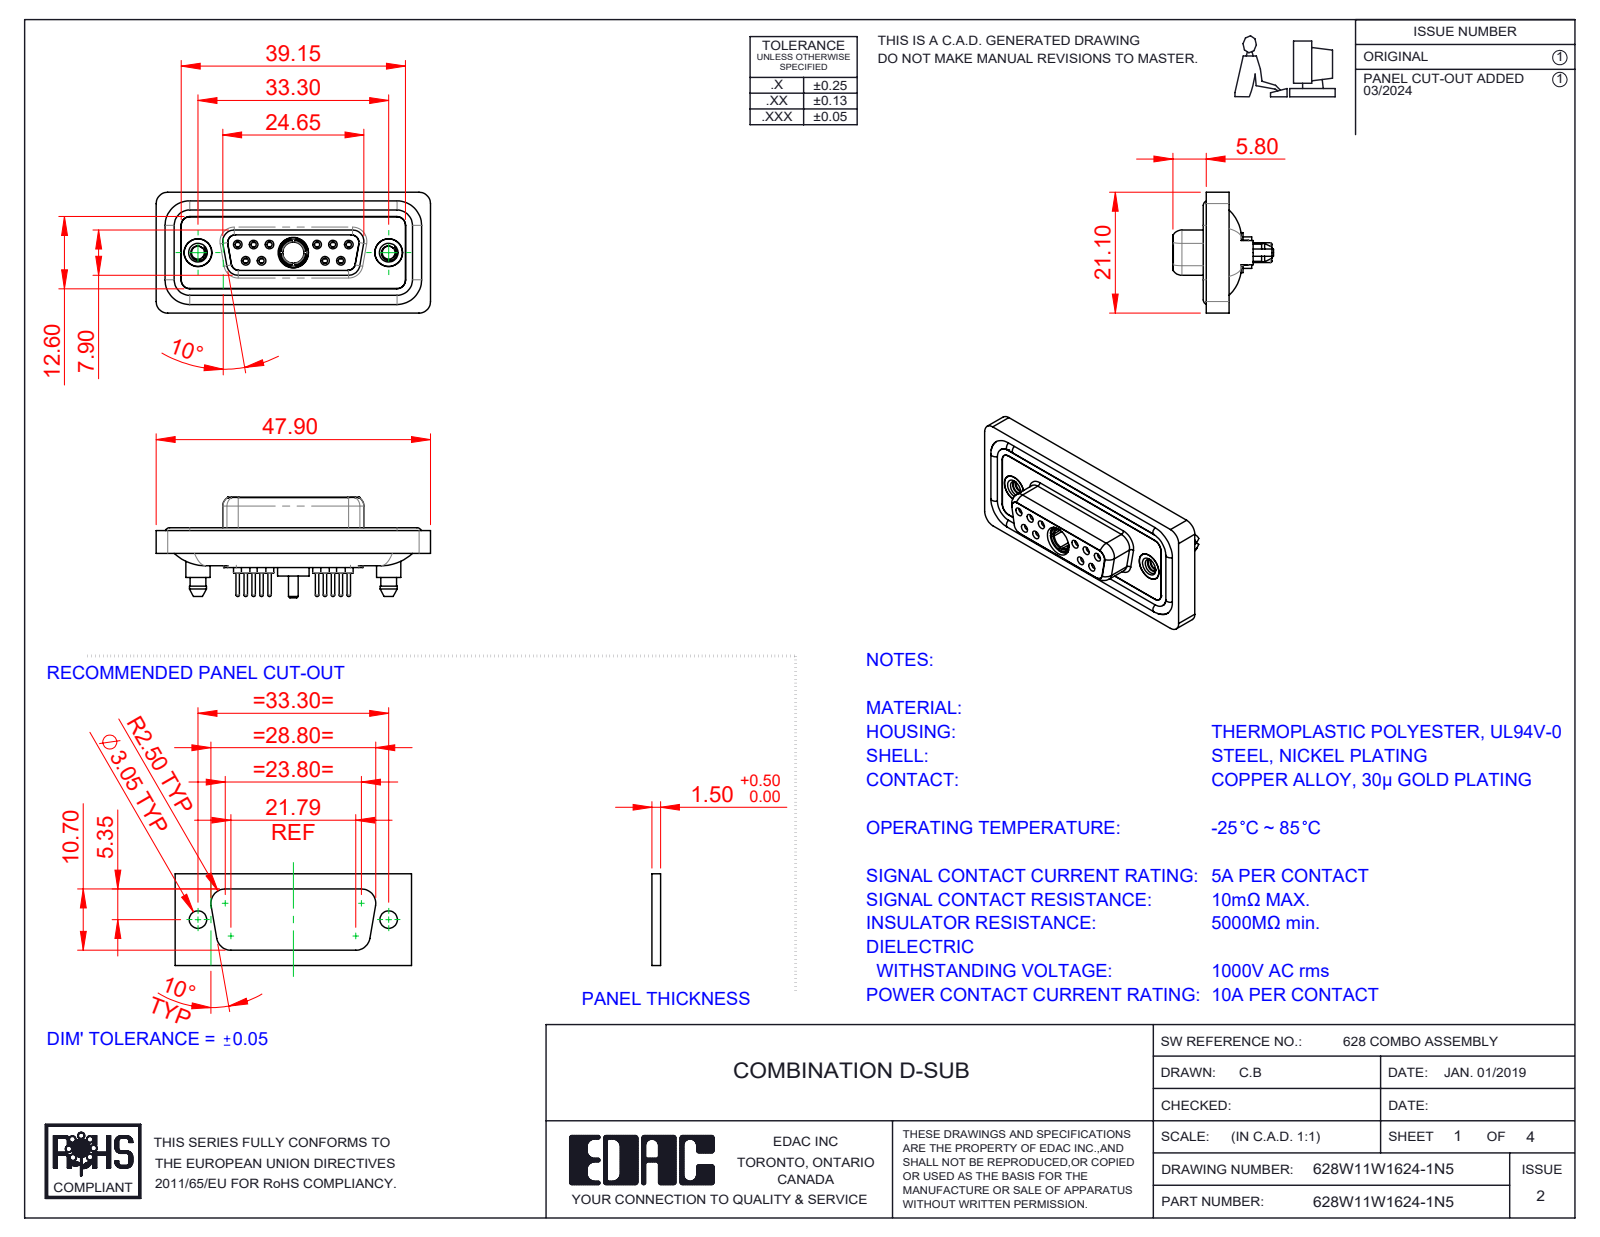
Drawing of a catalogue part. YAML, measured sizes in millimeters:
part_name: "628Combo Contact Row 1_24; 628W11W1624-1N5; 628Combo Shell Rear_15 Contacts; 628Combo Waterproof Housing_15 Contacts (+5 more)"
step_written_by: "SolidWorks 2023 (CONFIG_CONTROL_DESIGN)"
units: millimeters
bodies: {solids: 19, faces: 1060, planar: 300, cylindrical: 433, other: 327}
overall_size: [47.9, 21.1, 17.55]
volume: 6246
surface_area: 10352
round_holes:
  - {diameter: 0.9, count: 10}
  - {diameter: 1.1, count: 10}
  - {diameter: 1.5, count: 10}
  - {diameter: 2, count: 10}
  - {diameter: 1.7, count: 6}
  - {diameter: 1.6, count: 4}
  - {diameter: 4.85, count: 3}
  - {diameter: 2.26, count: 2}
  - {diameter: 4, count: 2}
  - {diameter: 4.05, count: 2}
  - {diameter: 5, count: 2}
  - {diameter: 3.7, count: 1}
round_bosses_or_shafts:
  - {diameter: 2.2, count: 10}
  - {diameter: 1.6, count: 10}
  - {diameter: 0.6, count: 10}
  - {diameter: 5.4, count: 2}
  - {diameter: 4.95, count: 2}
  - {diameter: 4.8, count: 2}
  - {diameter: 4.25, count: 2}
  - {diameter: 5.5, count: 1}
partial_cylinders:
  - {radius: 1.5, count: 24}
  - {radius: 2, count: 20}
  - {radius: 1.35, count: 12}
  - {radius: 1.6, count: 10}
  - {radius: 0.25, count: 4}
  - {radius: 0.5, count: 4}
  - {radius: 0.6, count: 4}
  - {radius: 0.65, count: 4}
face_to_face_distances: [0.4, 1.6, 1.8, 2.9, 0.5, 1.1, 5.65, 7.45, 6.6, 7.05]
hole_center_spacings: [3.16, 2.77, 13.85, 11.08, 16.62, 5.03, 5.04, 5.54]
